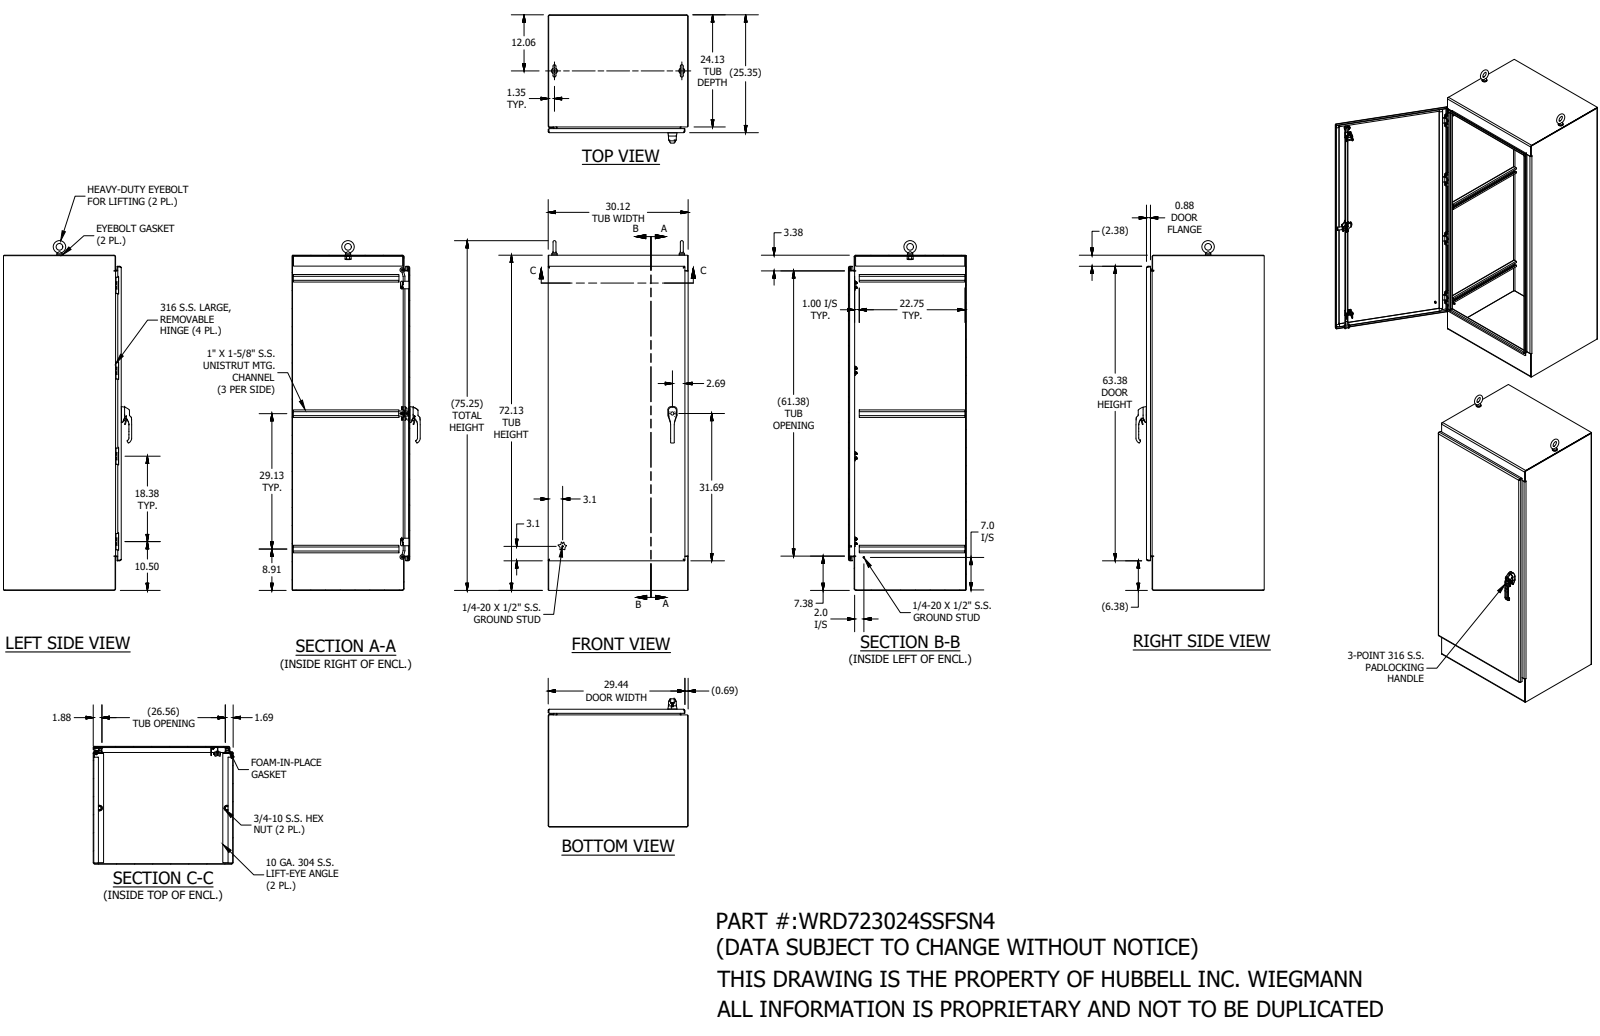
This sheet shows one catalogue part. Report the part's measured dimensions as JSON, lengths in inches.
{"part_name": "WRD723024SSFSN4", "step_written_by": "SolidWorks 2019 (AUTOMOTIVE_DESIGN)", "units": "inches", "bodies": {"solids": 103, "faces": 3881, "planar": 1580, "cylindrical": 1362, "other": 939}, "overall_size": [75.248, 30.129, 27.598], "volume_in3": 1183, "surface_area_in2": 22085, "round_holes": [[0.14, 24], [0.195, 8], [0.262, 8], [0.266, 8], [0.294, 8], [0.65, 8], [0.136, 4], [0.164, 4], [0.187, 4], [0.201, 4], [0.213, 3], [0.281, 3]], "round_bosses_or_shafts": [[0.625, 8], [0.25, 7], [0.237, 4], [0.236, 3], [1.25, 2], [1.12, 2], [1, 2], [0.75, 2]], "partial_cylinders_radius": [[0.02, 172], [0.012, 114], [0.125, 34], [0.019, 21], [0.062, 18], [0.05, 14], [0.063, 14], [0.079, 14]], "face_to_face_distances": [0.104, 30.021, 25.245, 25.141, 0.104, 29.917, 25.349, 25.245, 30.125, 72.021], "hole_center_spacings": [0.018, 0.023, 0.024, 0.38, 0.76, 1, 18.375, 36.75]}
